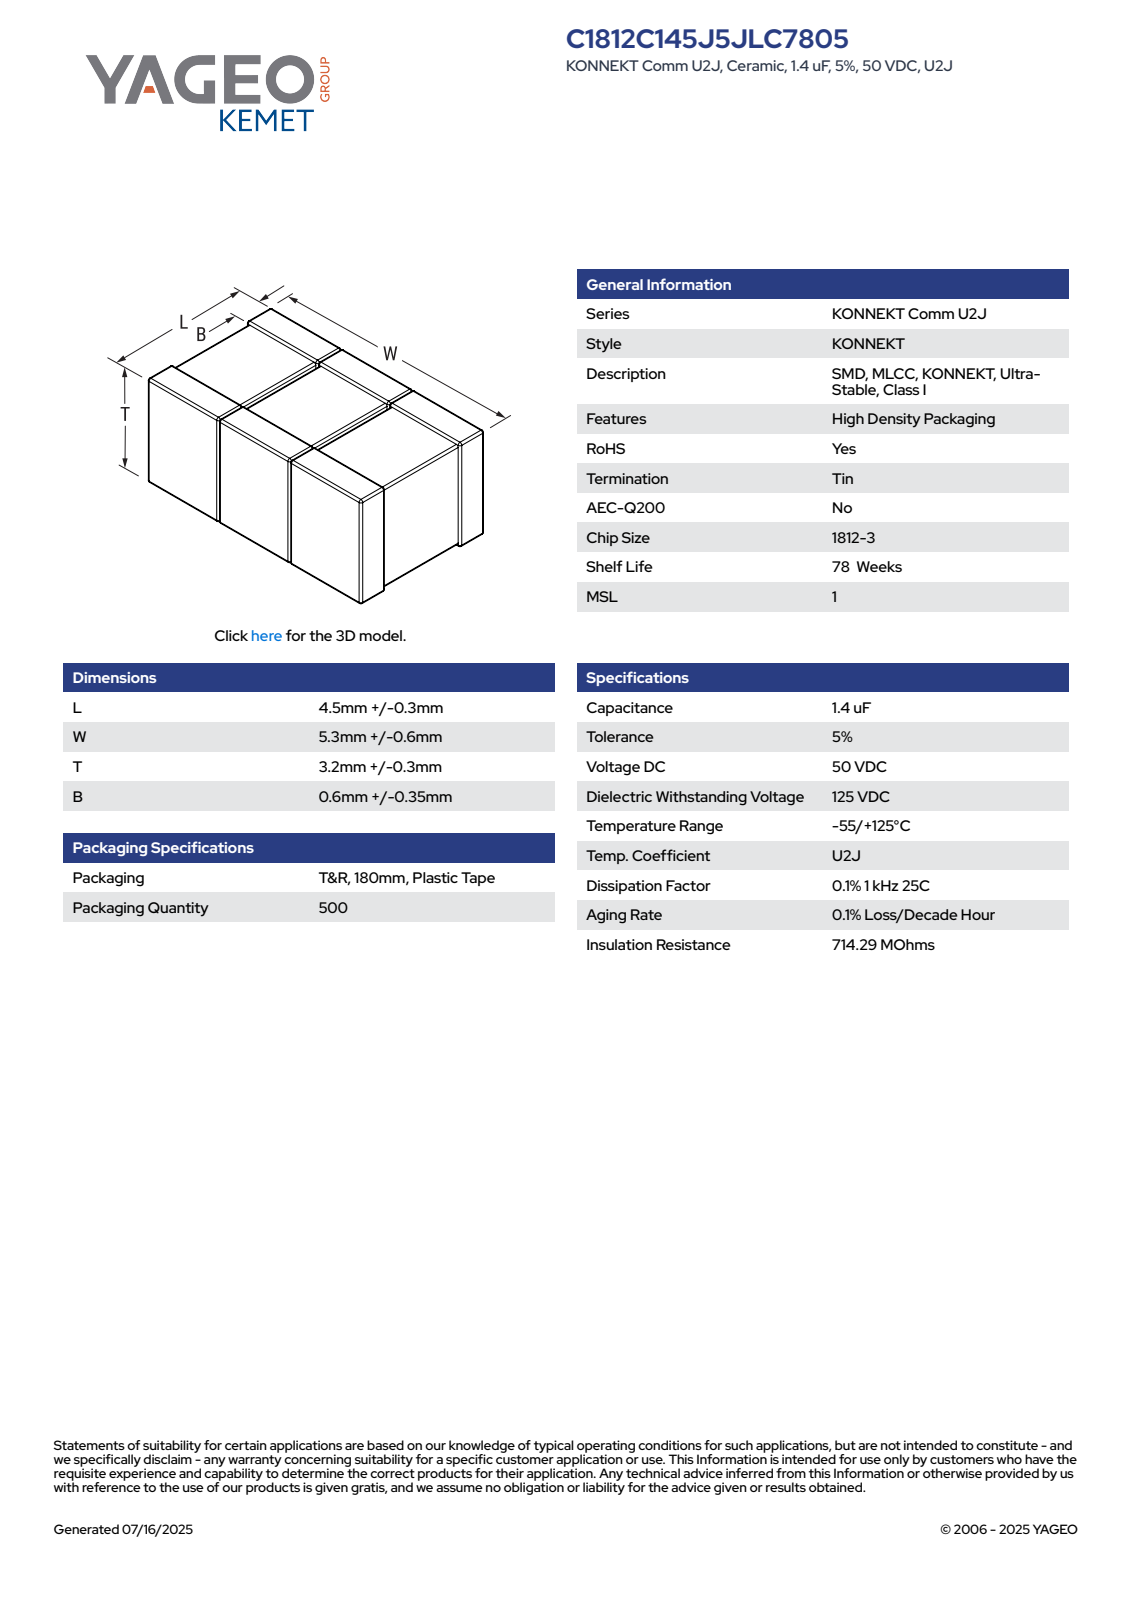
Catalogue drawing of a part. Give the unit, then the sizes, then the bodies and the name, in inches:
Units: inches
Overall size (bounding box): 0.232 × 0.189 × 0.138
Main face-to-face distances: 0.077, 0.075, 0.078, 0.152, 0.155, 0.08, 0.074, 0.072, 0.149, 0.189
Volume: 0.006 in³ · Surface area: 0.304 in²
Bodies: 12 solids, 351 faces (213 planar, 90 cylindrical, 48 other)
Part name (STEP PRODUCT): CCSS_K3LL_1812-3_L4.8W5.9B0.95T3.5
STEP written by: SolidWorks 2021 (AUTOMOTIVE_DESIGN)
